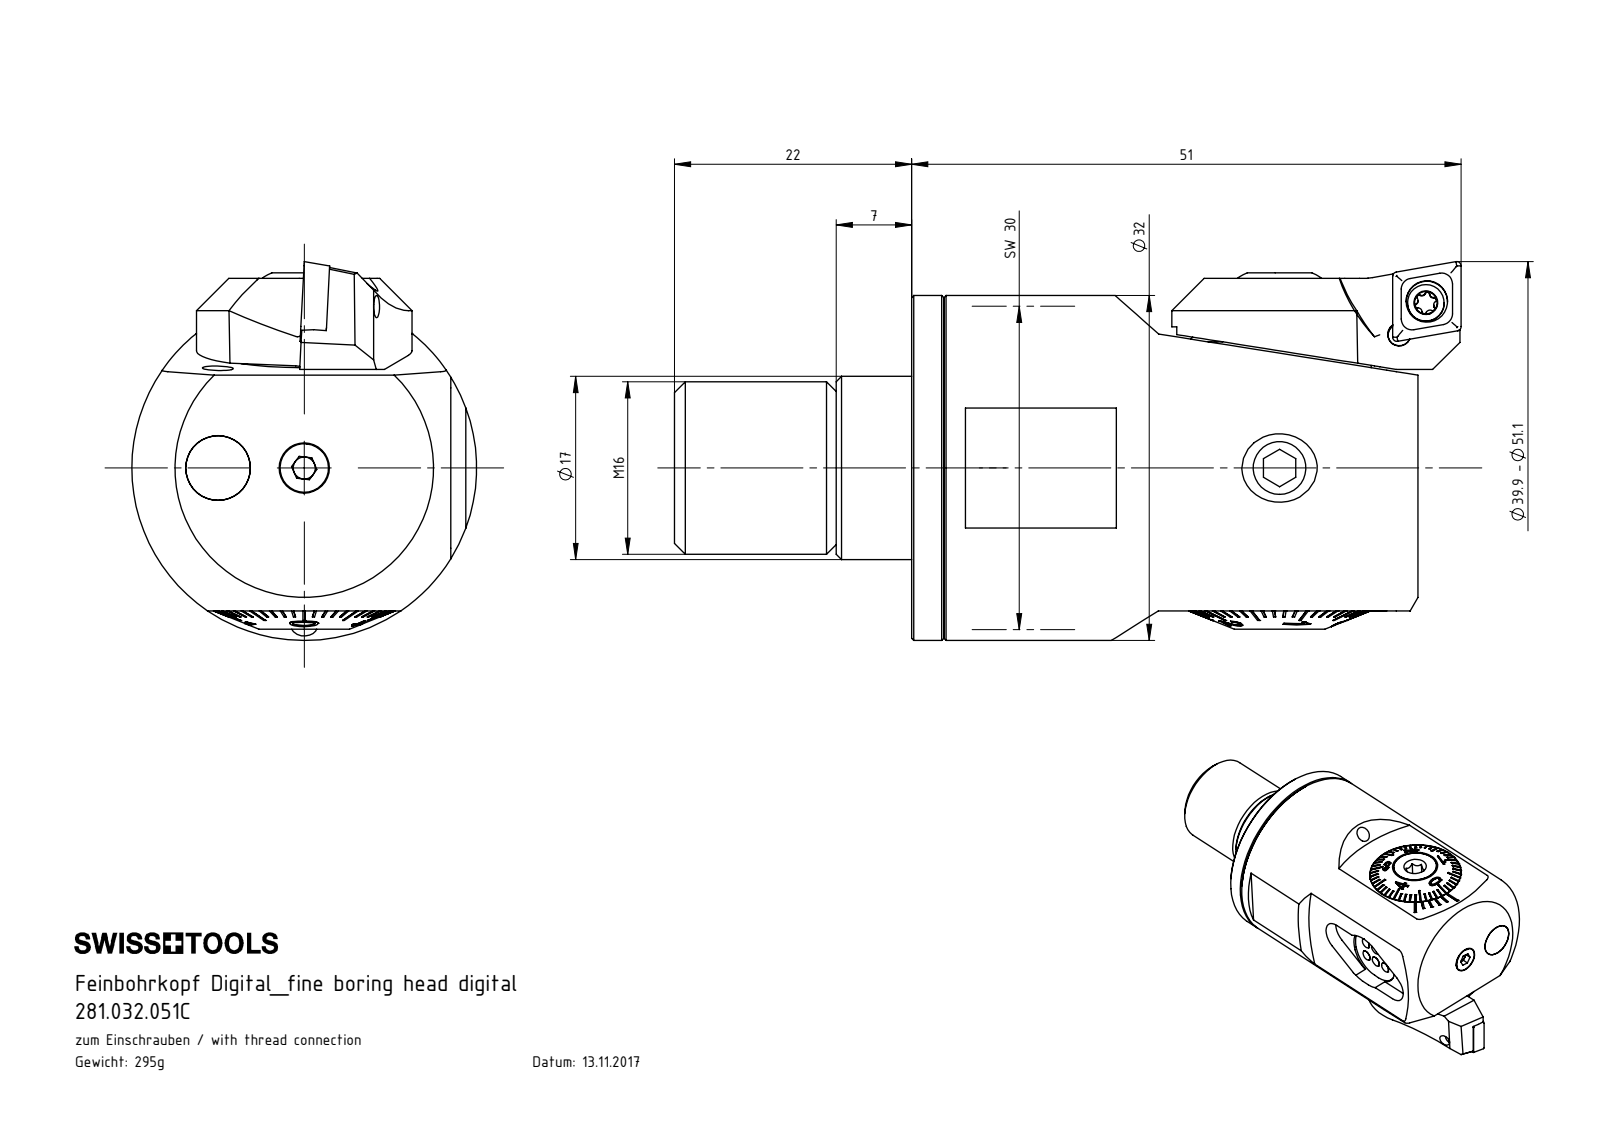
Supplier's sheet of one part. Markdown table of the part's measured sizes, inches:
| quantity | value |
| --- | --- |
| part name | F32-BG2.014.012_A; F32-BG1.DA1.017_A_Aktuell 0.6.2014-Mx1.3; F32-BG3.006.026_A; HP5-F32.DA1.051_A (+8 more) |
| STEP written by | SolidWorks 2017 (CONFIG_CONTROL_DESIGN) |
| units | inches |
| bodies | 22 solids, 931 faces (412 planar, 201 cylindrical, 318 other) |
| overall size | 2.874 × 1.384 × 1.26 |
| volume | 2.311 in³ |
| surface area | 32.21 in² |
| round holes (diameter × count) | 0.098 × 5, 0.081 × 2, 0.197 × 2, 0.669 × 2, 0.028 × 1, 0.083 × 1, 0.106 × 1, 0.11 × 1, 0.114 × 1, 0.118 × 1, 0.13 × 1, 0.152 × 1 |
| round bosses / shafts (diameter × count) | 0.075 × 6, 0.236 × 2, 0.098 × 2, 1.26 × 1, 0.669 × 1, 0.663 × 1, 0.63 × 1, 0.577 × 1 |
| partial cylindrical surfaces (radius × count) | 0.008 × 6, 0.014 × 5, 0.02 × 4, 0.043 × 3, 0.047 × 3, 0.069 × 2, 0.102 × 2, 0.122 × 2 |
| main face-to-face distances | 0.118, 1.85, 1.732, 0.177, 0.998, 0.821, 0.315, 0.217, 0.059, 0.146 |
| hole center spacings | 0.102, 0.112, 0.151, 0.157, 0.224, 0.315, 0.46, 0.99 |
